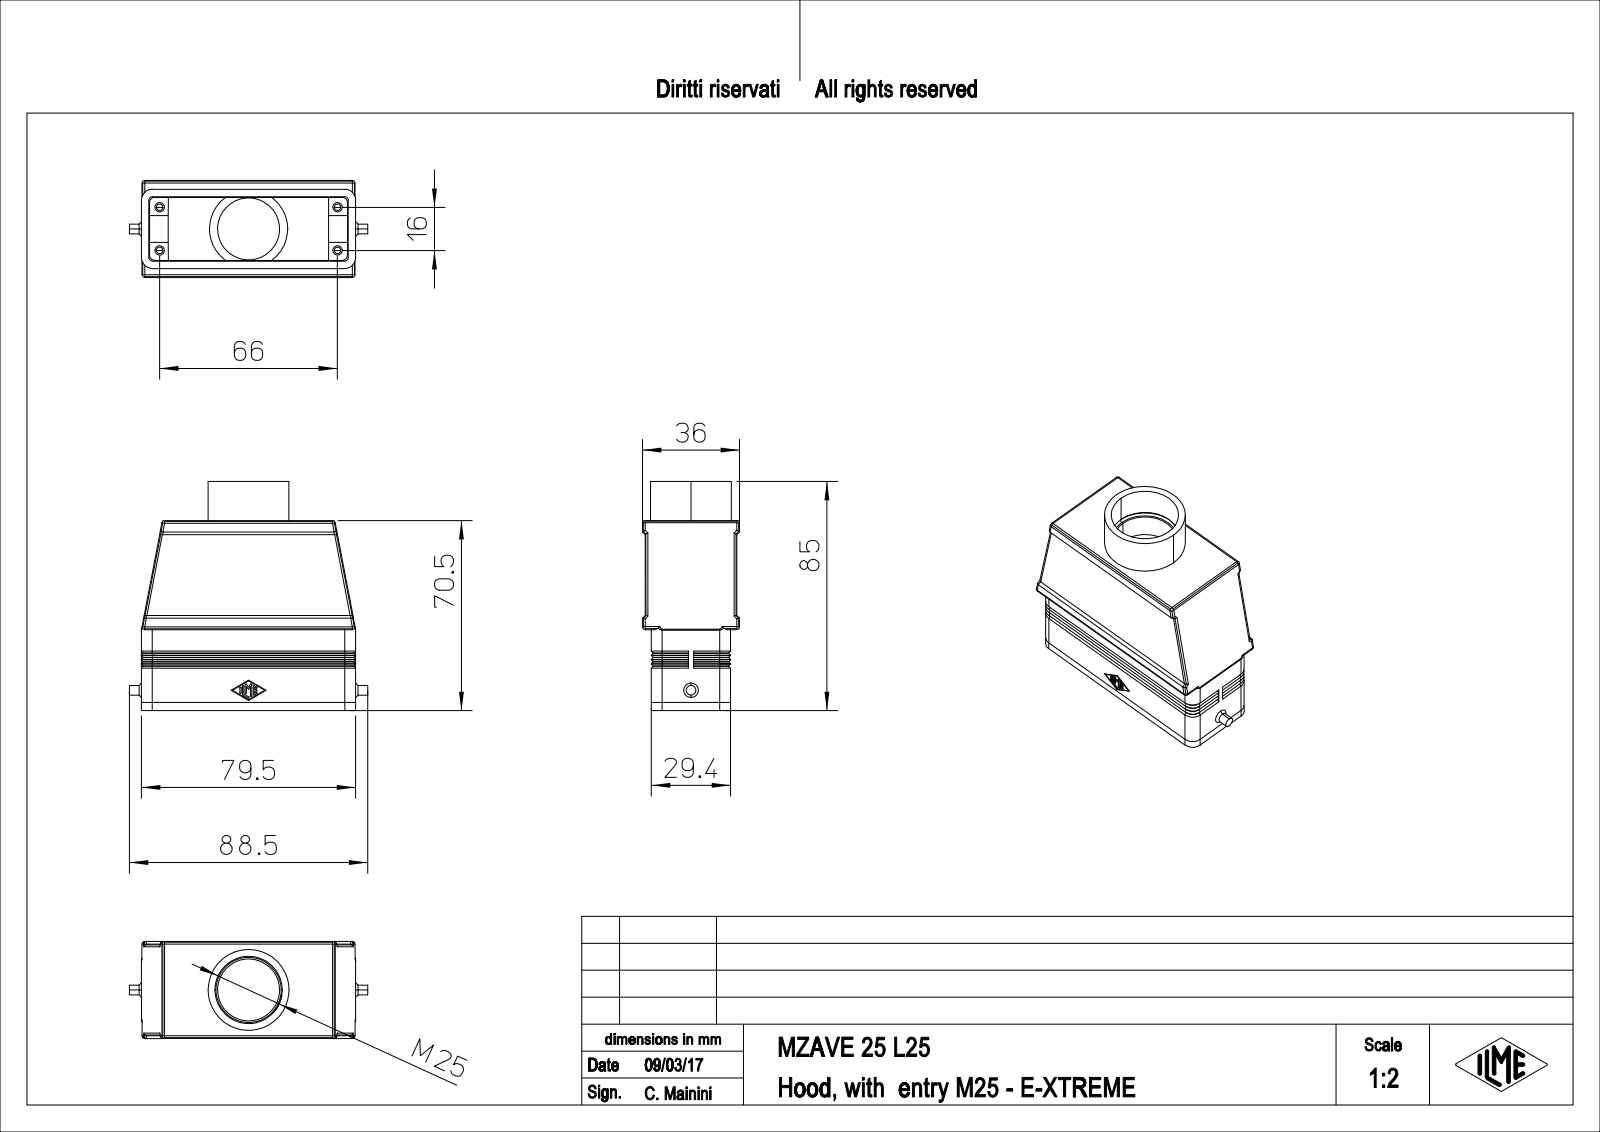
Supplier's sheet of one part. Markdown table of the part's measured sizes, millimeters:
| quantity | value |
| --- | --- |
| part name | MZAVE_25_L25 |
| STEP written by | PTC Creo Elements/Direct Modeling 19.0E 27-Jun-2016 (C) Parametric Technology GmbH (AUTOMOTIVE_DESIGN) |
| units | millimeters |
| bodies | 1 solid, 410 faces (194 planar, 156 cylindrical, 60 other) |
| overall size | 88.5 × 85 × 36 |
| volume | 69 472 mm³ |
| surface area | 35 438 mm² |
| round holes (diameter × count) | 2.46 × 4, 3.5 × 4, 23 × 1, 25 × 1 |
| round bosses / shafts (diameter × count) | 30 × 1, 3.6 × 1 |
| partial cylindrical surfaces (radius × count) | 1 × 24, 0.25 × 14, 4 × 8, 2 × 6, 1.25 × 4, 3.3 × 4, 14.5 × 1 |
| main face-to-face distances | 3, 28.7, 5.3, 23.4, 2.3, 31.7, 26.4, 34, 29.4, 10 |
| hole center spacings | 33.96, 16, 66, 67.91 |
